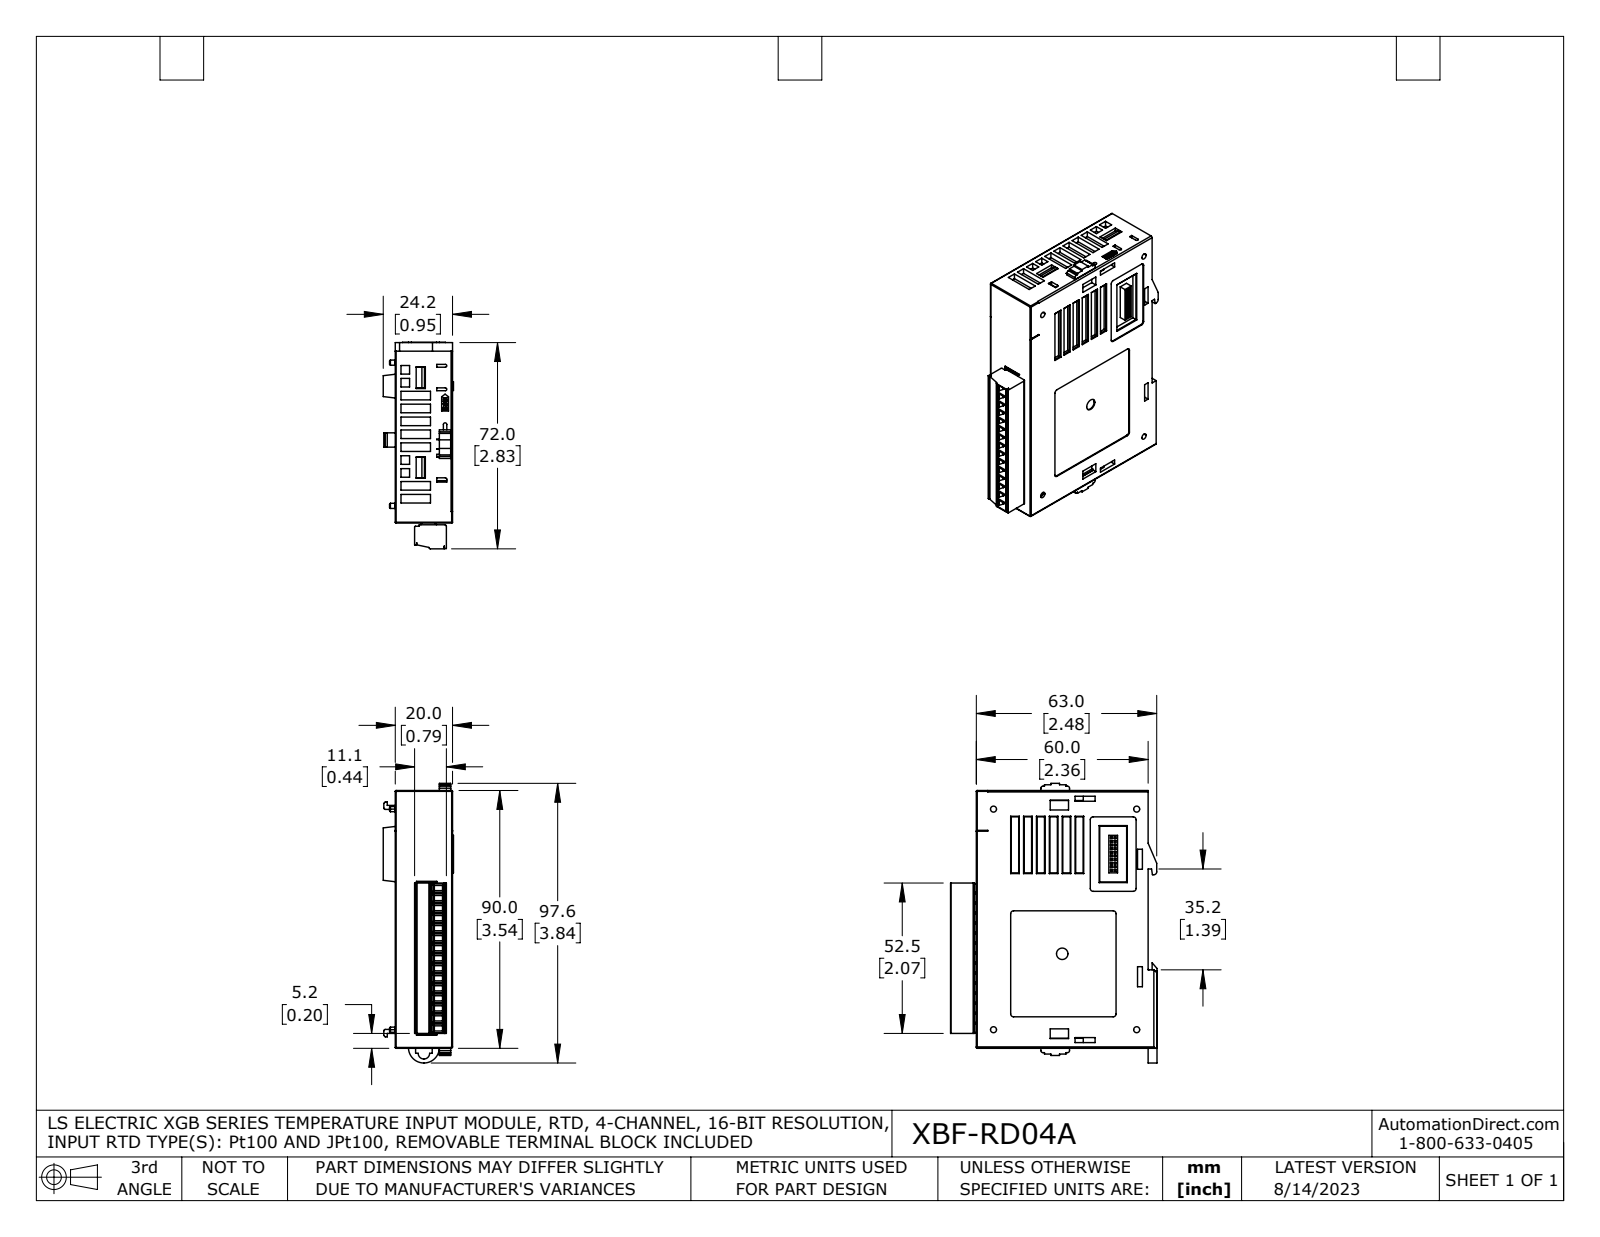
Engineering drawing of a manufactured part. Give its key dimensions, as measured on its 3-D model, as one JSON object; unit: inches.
{"part_name": "XBF-RD04A nc din clip 6 bad faces cut1 coord fxt", "step_written_by": "SolidWorks 2021 (AUTOMOTIVE_DESIGN)", "units": "inches", "bodies": {"solids": 1, "faces": 2818, "planar": 1979, "cylindrical": 581, "other": 258}, "overall_size": [3.844, 2.839, 0.966], "volume_in3": 6.657, "surface_area_in2": 48.18, "round_holes": [[0.047, 15], [0.108, 15], [0.116, 15], [0.083, 4], [0.071, 2], [0.157, 1]], "round_bosses_or_shafts": [[0.11, 15], [0.071, 6]], "partial_cylinders_radius": [[0.008, 62], [0.004, 60], [0.012, 48], [0.02, 21], [0.062, 15], [0.071, 15], [0.039, 11], [0.031, 6]], "face_to_face_distances": [0.787, 0.079, 0.039, 0.776, 0.709, 2.362, 0.748, 0.669, 0.067, 0.047], "hole_center_spacings": [0.138, 0.276, 0.413, 0.551, 0.689, 0.827, 0.965, 1.102]}
